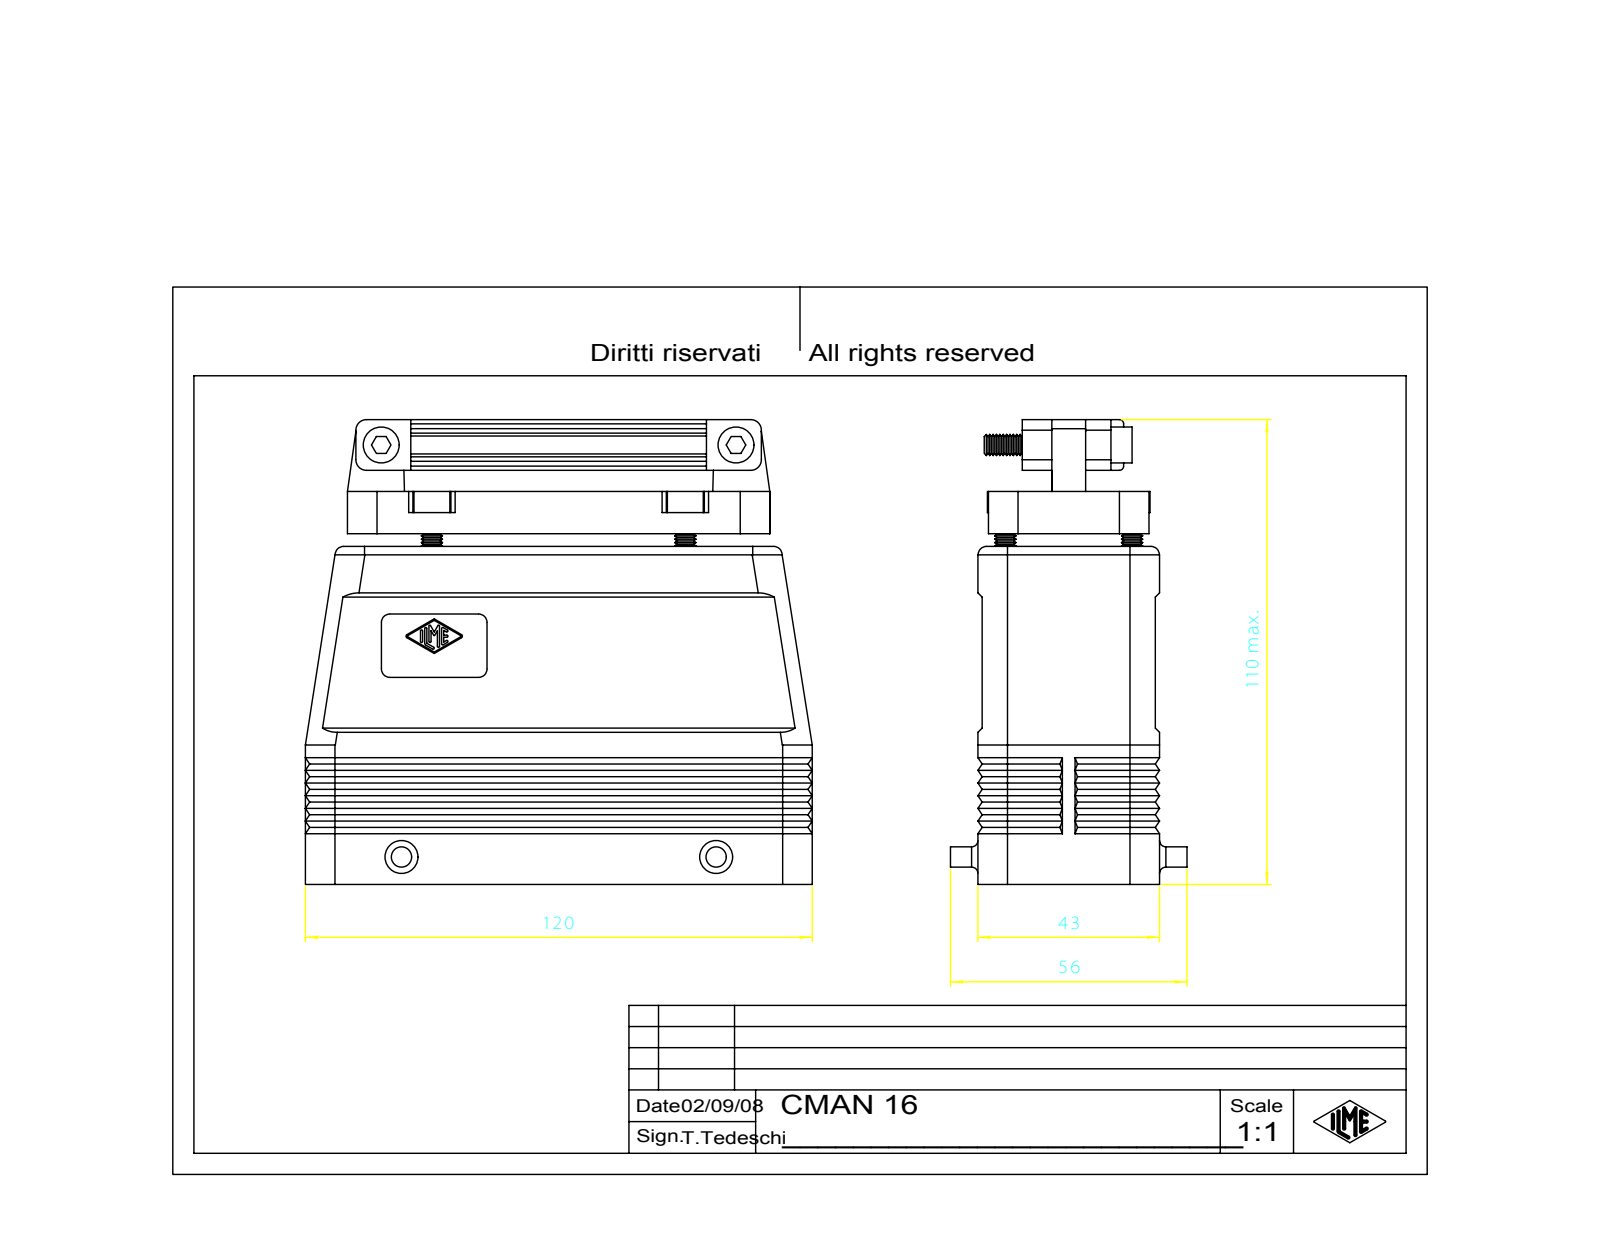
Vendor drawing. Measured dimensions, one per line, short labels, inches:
name: CMAN_16
written by: OneSpace Modeling 15.50B 03-Nov-2007 (C) CoCreate Software GmbH (AUTOMOTIVE_DESIGN)
unit: in
bodies: 1 solid, 1061 faces (366 planar, 203 cylindrical, 492 other)
size: 4.724 × 4.331 × 2.205
volume: 8.368 in³; area: 126.9 in²
holes: 6× ⌀0.217, 4× ⌀0.118, 4× ⌀0.197, 2× ⌀0.169
bosses: 6× ⌀0.335, 2× ⌀0.197, 2× ⌀0.189
rounds: 14× R0.039, 12× R0.079, 12× R0.276, 11× R0.01, 7× R0.098, 4× R0.059, 4× R0.165, 4× R0.177
face distances: 0.11, 1.472, 0.071, 1.543, 0.039, 1.654, 1.583, 0.394, 0.276, 0.591
hole spacings: 0.867, 0.87, 1.063, 1.181, 1.417, 1.419, 2.362, 2.641
